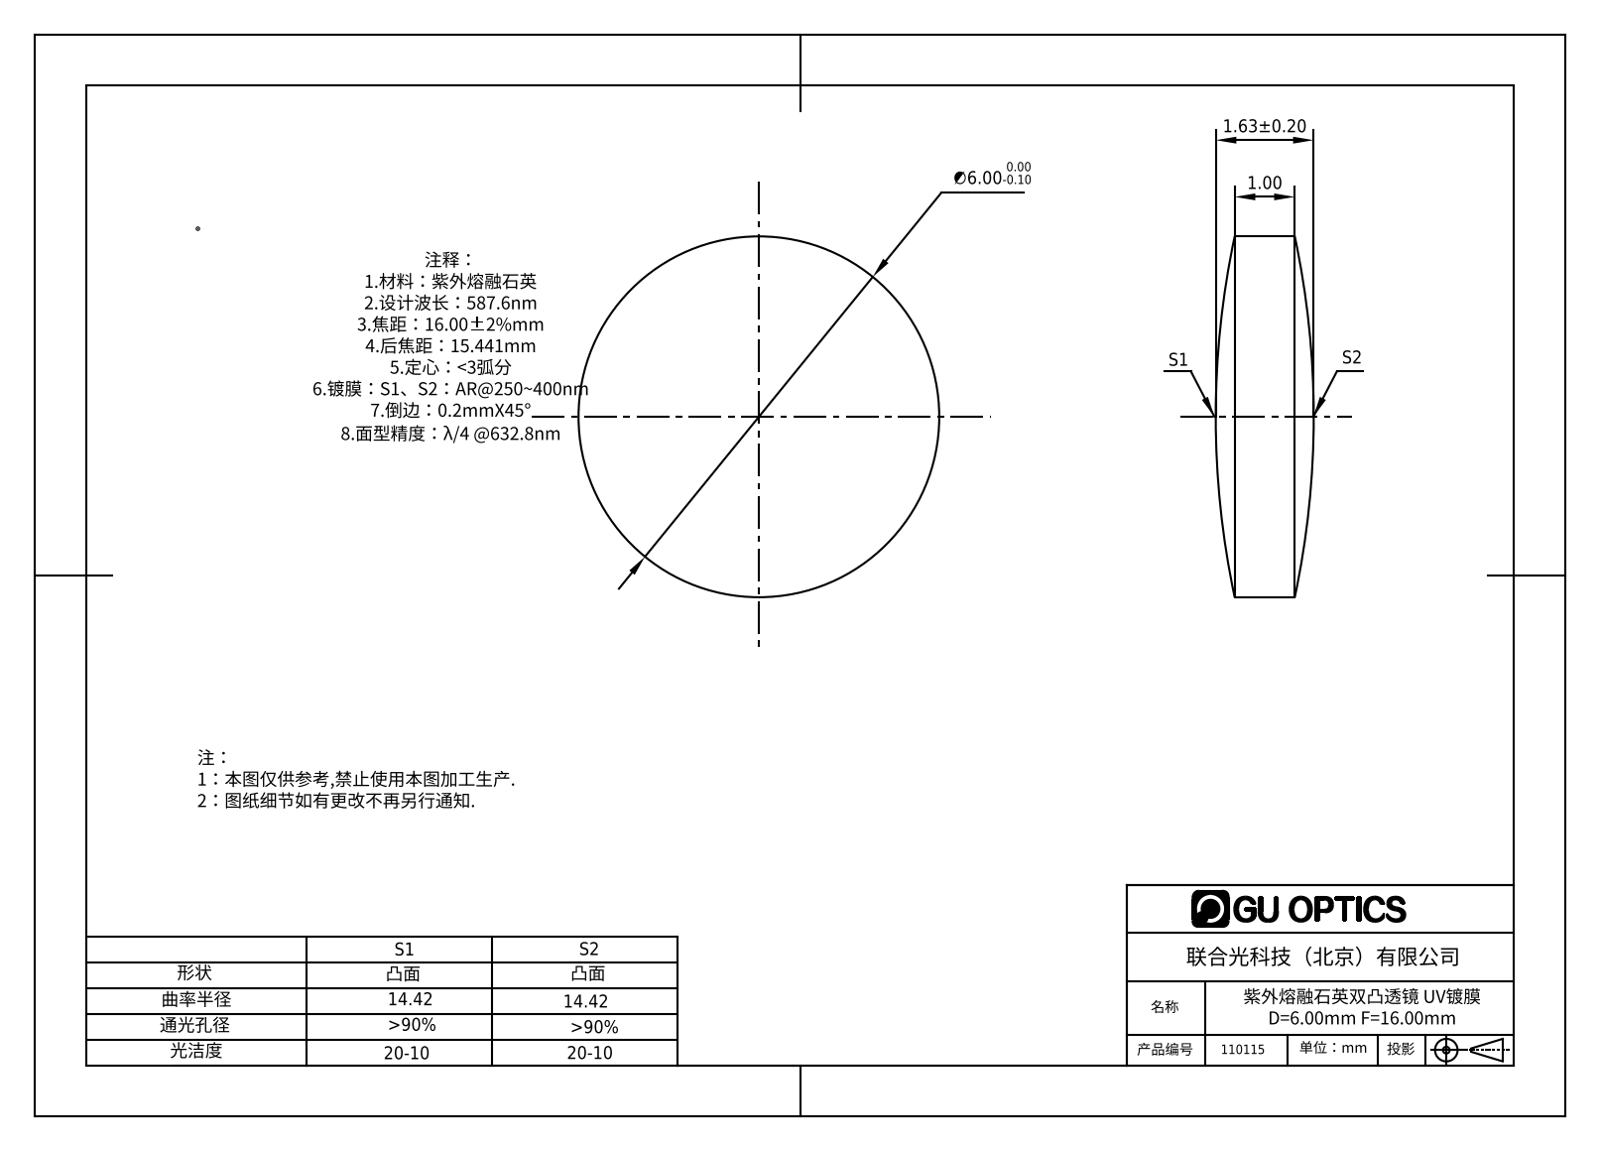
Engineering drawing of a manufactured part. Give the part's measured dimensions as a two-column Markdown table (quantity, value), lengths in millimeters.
| quantity | value |
| --- | --- |
| part name | 110091 |
| STEP written by | SolidWorks 2016 (CONFIG_CONTROL_DESIGN) |
| units | millimeters |
| bodies | 1 solid, 6 faces (0 planar, 2 cylindrical, 4 other) |
| overall size | 6 × 6 × 1.63 |
| volume | 37 mm³ |
| surface area | 76 mm² |
| round bosses / shafts (diameter × count) | 6 × 1 |
